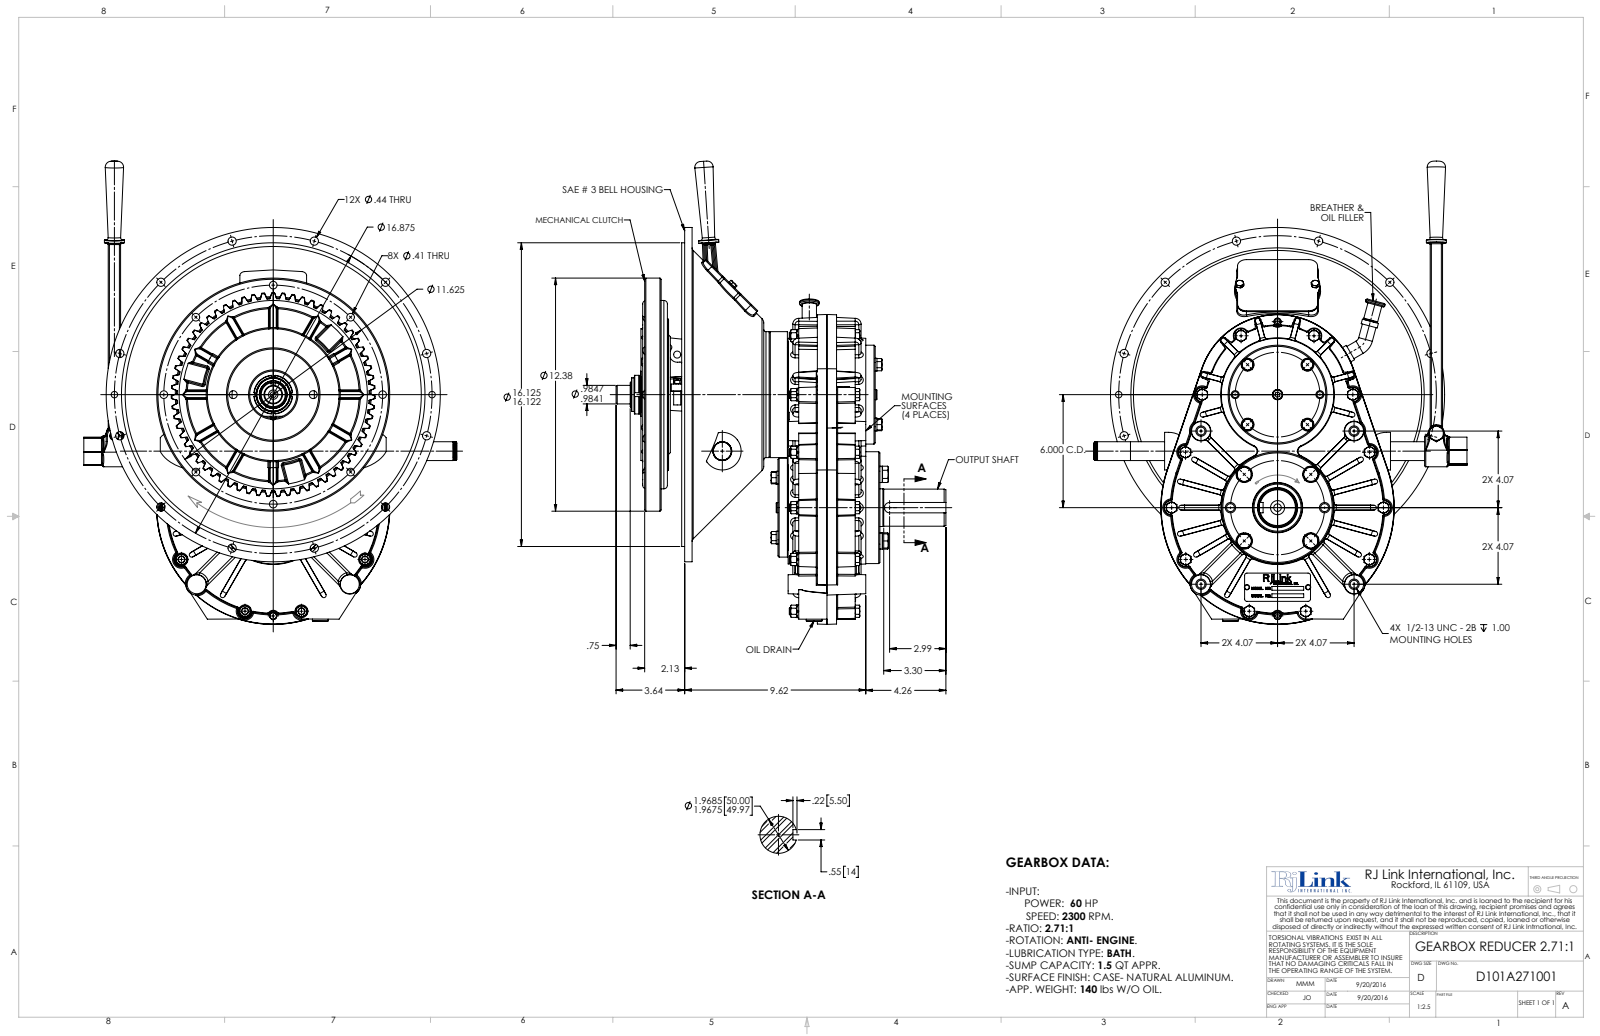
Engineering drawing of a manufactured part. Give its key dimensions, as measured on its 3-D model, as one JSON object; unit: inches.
{"part_name": "WFL5000004; SH K-_SH K-21507; PPSKM.50-14; DS90081A106 (+8 more)", "step_written_by": "SolidWorks 2016 (AUTOMOTIVE_DESIGN)", "units": "inches", "bodies": {"solids": 108, "faces": 6182, "planar": 2154, "cylindrical": 1632, "other": 2396}, "overall_size": [24.596, 19.813, 17.522], "volume_in3": 448.8, "surface_area_in2": 3254, "round_holes": [[0.313, 37], [0.385, 20], [0.422, 16], [0.438, 16], [0.375, 14], [0.406, 12], [0.406, 8], [0.413, 8], [0.531, 8], [0.59, 8], [0.512, 4], [0.531, 4]], "round_bosses_or_shafts": [[0.375, 28], [0.683, 20], [0.562, 12], [0.75, 10], [0.5, 9], [0.563, 8], [0.406, 8], [0.869, 4]], "partial_cylinders_radius": [[1.796, 126], [0.063, 59], [0.125, 50], [0.062, 47], [0.188, 9], [0.06, 6], [0.25, 6], [0.08, 5]], "face_to_face_distances": [1.5, 0.313, 2.687, 1.187, 0.563, 2.063, 3.563, 0.875, 3.25, 3], "hole_center_spacings": [6.27, 2.25, 2.5, 1.722, 1.913, 2.887, 3.182, 3.25]}
